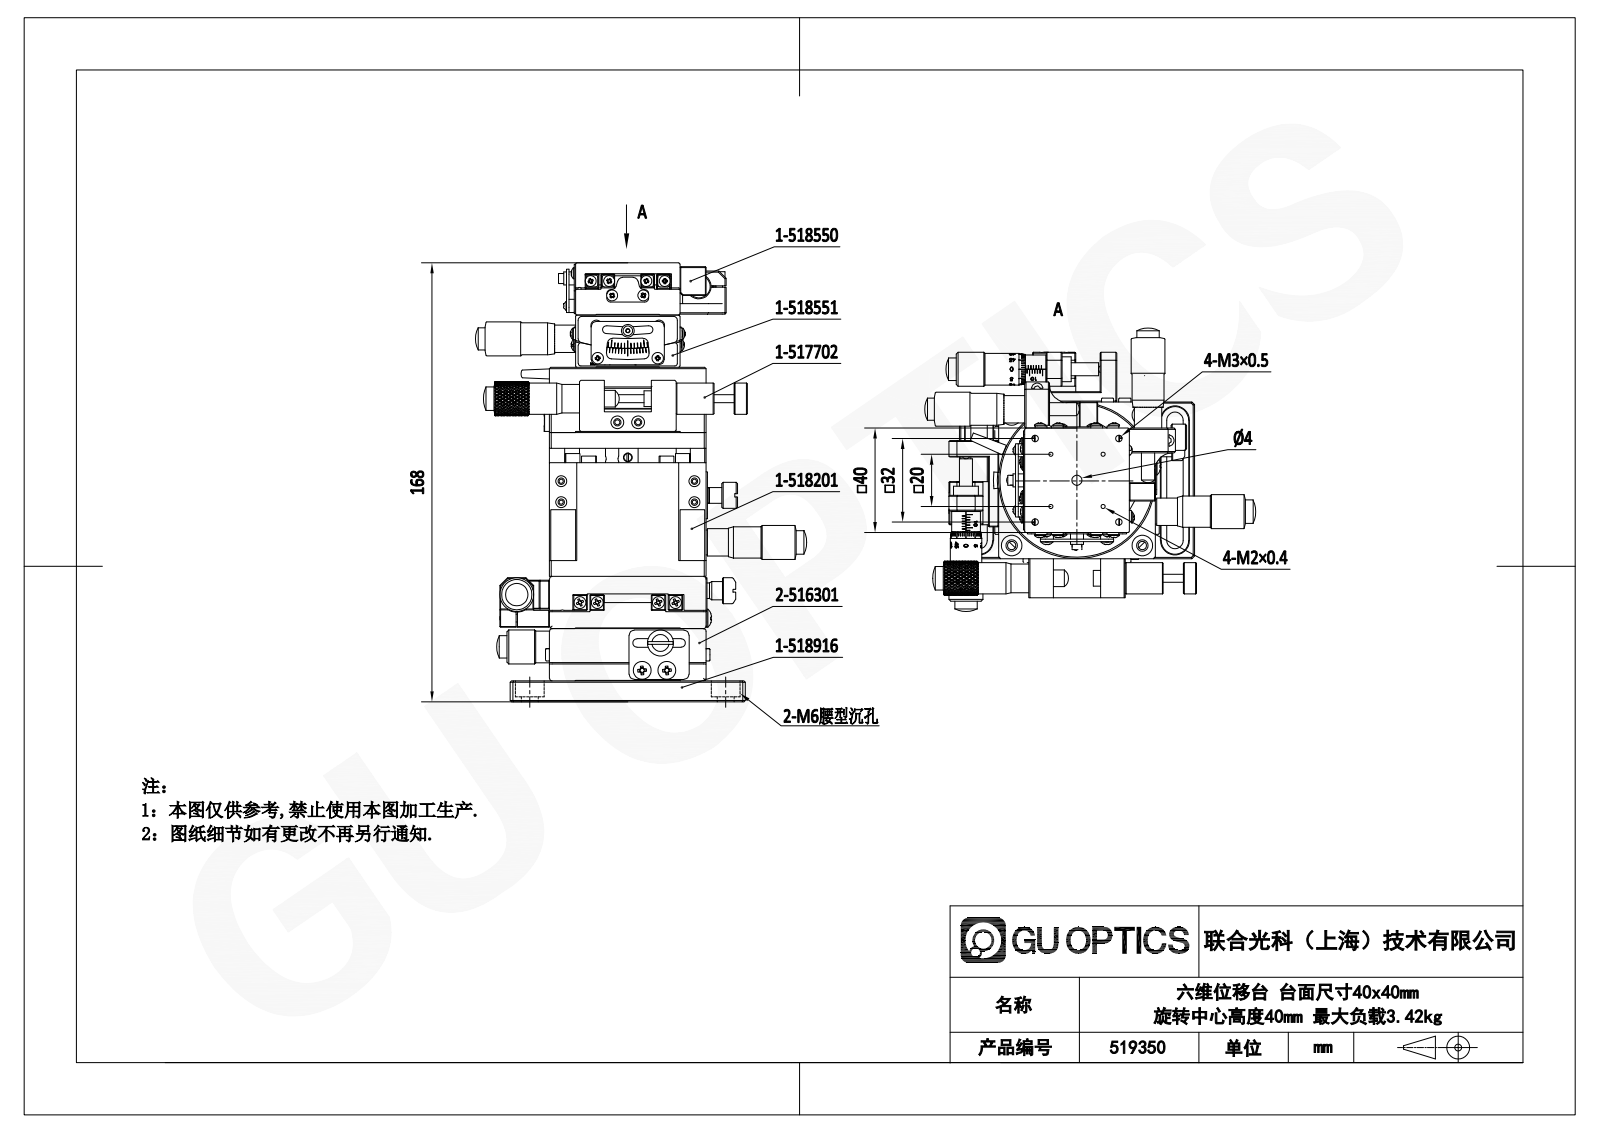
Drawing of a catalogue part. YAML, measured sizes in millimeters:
part_name: "518550; 516301; 519350; 518551 (+3 more)"
step_written_by: "SolidWorks 2020 (CONFIG_CONTROL_DESIGN)"
units: millimeters
bodies: {solids: 26, faces: 7821, planar: 3845, cylindrical: 1327, other: 2649}
overall_size: [168, 126.8, 116.3]
volume: 404371
surface_area: 187881
round_holes:
  - {diameter: 6, count: 19}
  - {diameter: 2.5, count: 18}
  - {diameter: 4, count: 16}
  - {diameter: 1.57, count: 15}
  - {diameter: 2.46, count: 14}
  - {diameter: 3.2, count: 12}
  - {diameter: 3.4, count: 12}
  - {diameter: 3.24, count: 8}
  - {diameter: 3.3, count: 8}
  - {diameter: 1.6, count: 6}
  - {diameter: 5, count: 6}
  - {diameter: 2.46, count: 4}
round_bosses_or_shafts:
  - {diameter: 4.2, count: 20}
  - {diameter: 5, count: 14}
  - {diameter: 1.57, count: 13}
  - {diameter: 3, count: 12}
  - {diameter: 2.5, count: 11}
  - {diameter: 5.5, count: 8}
  - {diameter: 4.7, count: 8}
  - {diameter: 6, count: 7}
partial_cylinders:
  - {radius: 0.5, count: 40}
  - {radius: 1, count: 40}
  - {radius: 0.8, count: 32}
  - {radius: 2, count: 32}
  - {radius: 1.5, count: 24}
  - {radius: 3, count: 12}
  - {radius: 1.75, count: 10}
  - {radius: 3.5, count: 5}
face_to_face_distances: [20, 0.5, 6.5, 60, 13, 40, 15, 7, 6.7, 6]
hole_center_spacings: [25, 20, 18.03, 35.36, 36.4, 15, 18.36, 26.68]
